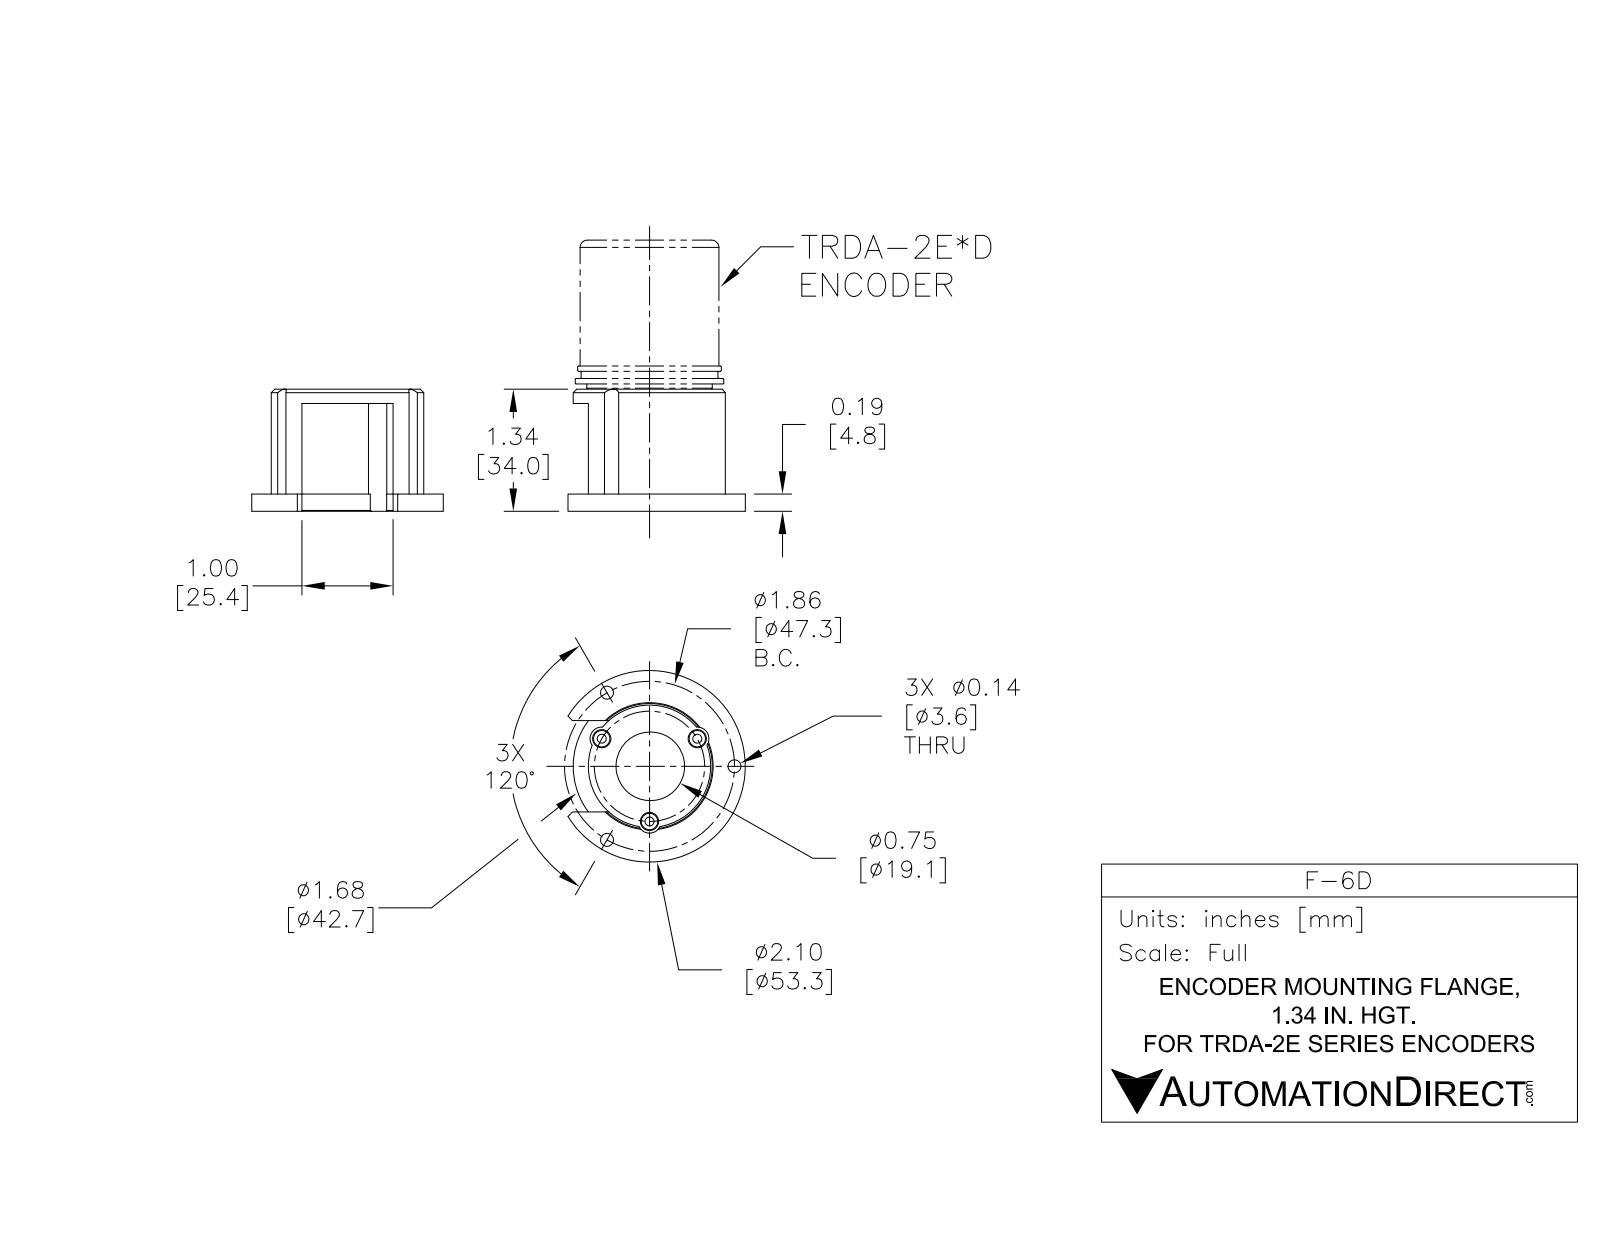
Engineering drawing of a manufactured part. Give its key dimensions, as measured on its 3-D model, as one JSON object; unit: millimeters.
{"part_name": "F-6D", "step_written_by": "SolidWorks 2016 (AUTOMOTIVE_DESIGN)", "units": "millimeters", "bodies": {"solids": 1, "faces": 68, "planar": 21, "cylindrical": 38, "other": 9}, "overall_size": [53.3, 49.18, 34], "volume_mm3": 18288, "surface_area_mm2": 10669, "round_holes": [[6.5, 6], [3.2, 3], [3.56, 3], [19.05, 1], [34.04, 1]], "round_bosses_or_shafts": [[53.3, 1], [42.67, 1]], "partial_cylinders_radius": [[17.46, 1]], "face_to_face_distances": [34, 4.83, 29.17, 30.4, 25.57, 3.6, 25.4, 0.5, 26.07, 29.97], "hole_center_spacings": [15.37, 23.65, 26.62, 40.96, 12.88, 28.2, 37.75, 12.89]}
